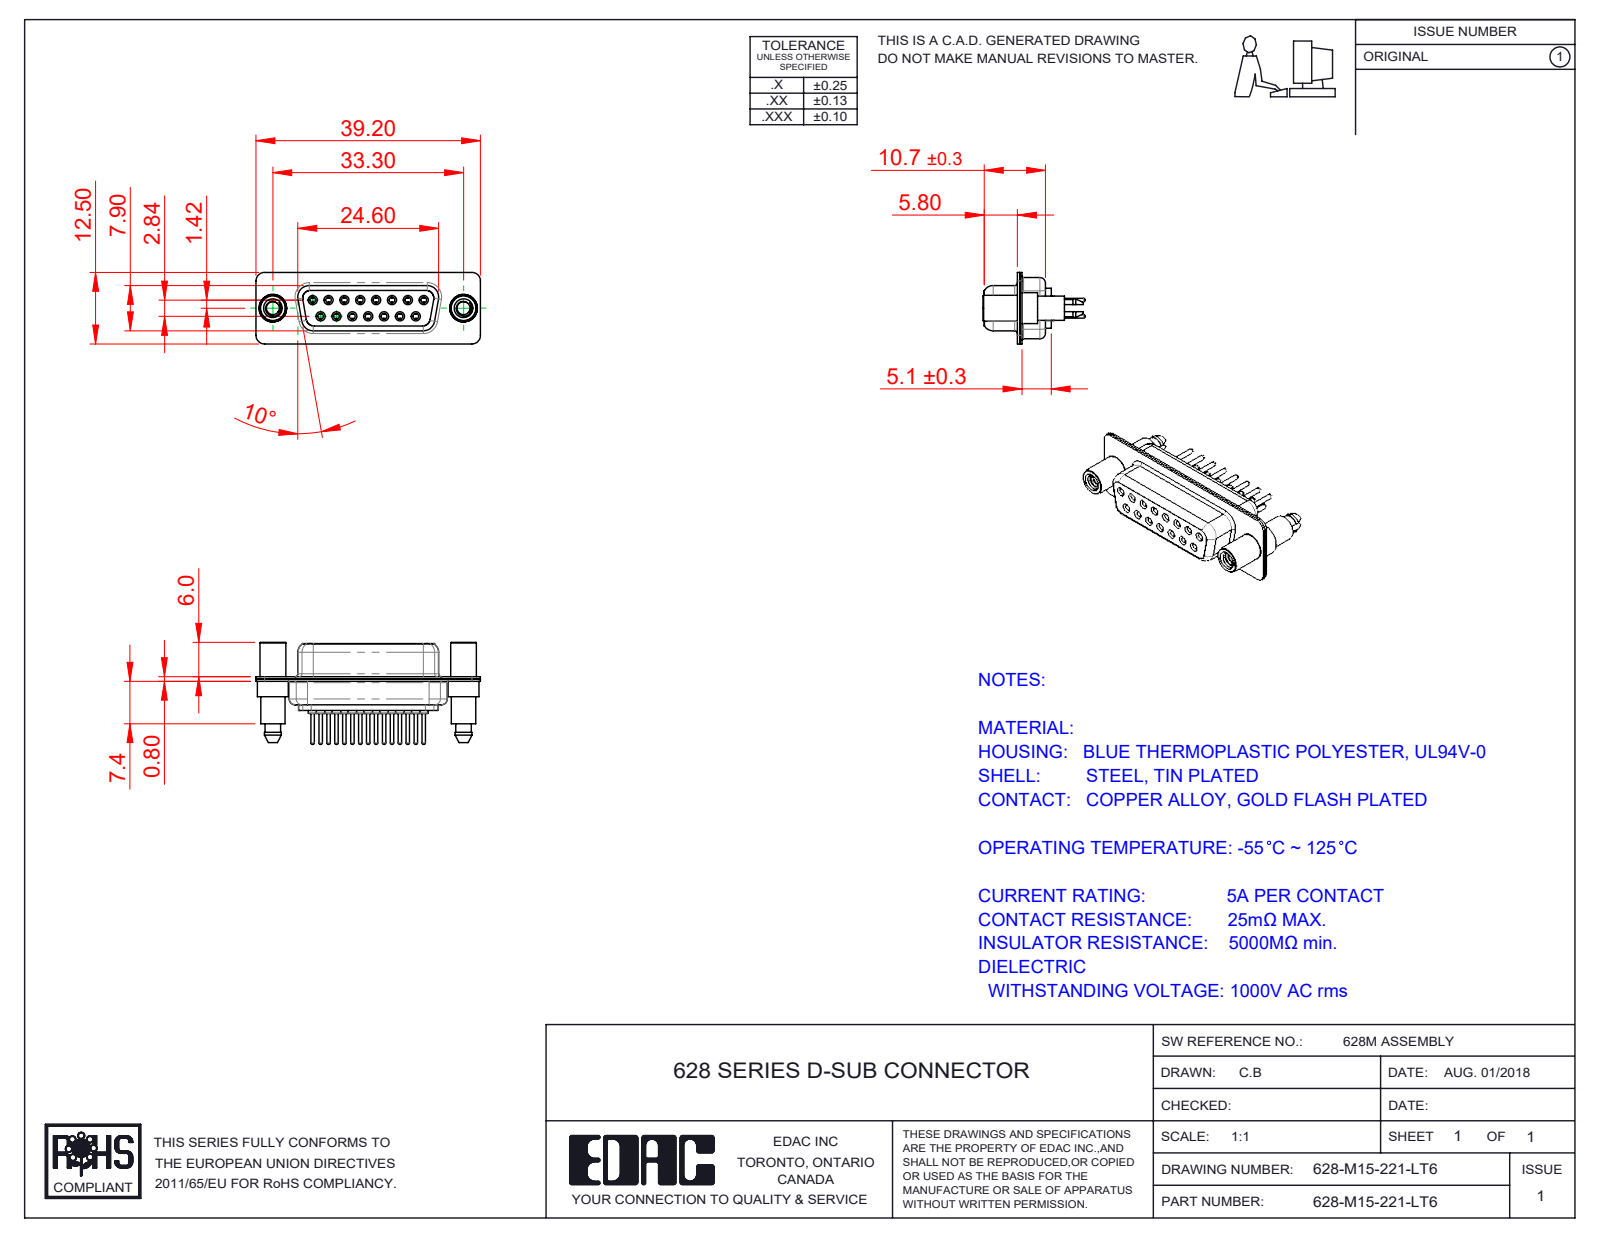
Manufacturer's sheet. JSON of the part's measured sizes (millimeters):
{"part_name": "628M Shell Front_15 Contacts; 628M Contact Row 1_21; 628M Housing_15 Contacts; 628-M15-221-LT6 (+3 more)", "step_written_by": "SolidWorks 2020 (CONFIG_CONTROL_DESIGN)", "units": "millimeters", "bodies": {"solids": 20, "faces": 1156, "planar": 310, "cylindrical": 450, "other": 396}, "overall_size": [39.2, 17.8, 12.5], "volume_mm3": 2810, "surface_area_mm2": 6667, "round_holes": [[1, 15], [1.1, 15], [1.7, 15], [1.8, 15], [2, 15], [2.26, 2], [4, 2], [4.8, 2]], "round_bosses_or_shafts": [[2.2, 15], [1.6, 15], [1.5, 15], [0.6, 15], [5.4, 2], [4.9, 2], [4.5, 2], [4.25, 2]], "partial_cylinders_radius": [[1.5, 18], [2, 12], [1.6, 10], [1.35, 8], [0.25, 4], [0.5, 4], [0.6, 4], [0.65, 4]], "face_to_face_distances": [0.4, 1.4, 0.45, 8.45, 1.8, 8.9, 6.2, 1, 7.05, 9.3], "hole_center_spacings": [3.16, 2.77, 5.54, 8.31, 11.08, 5.03, 5.04, 7.48]}
